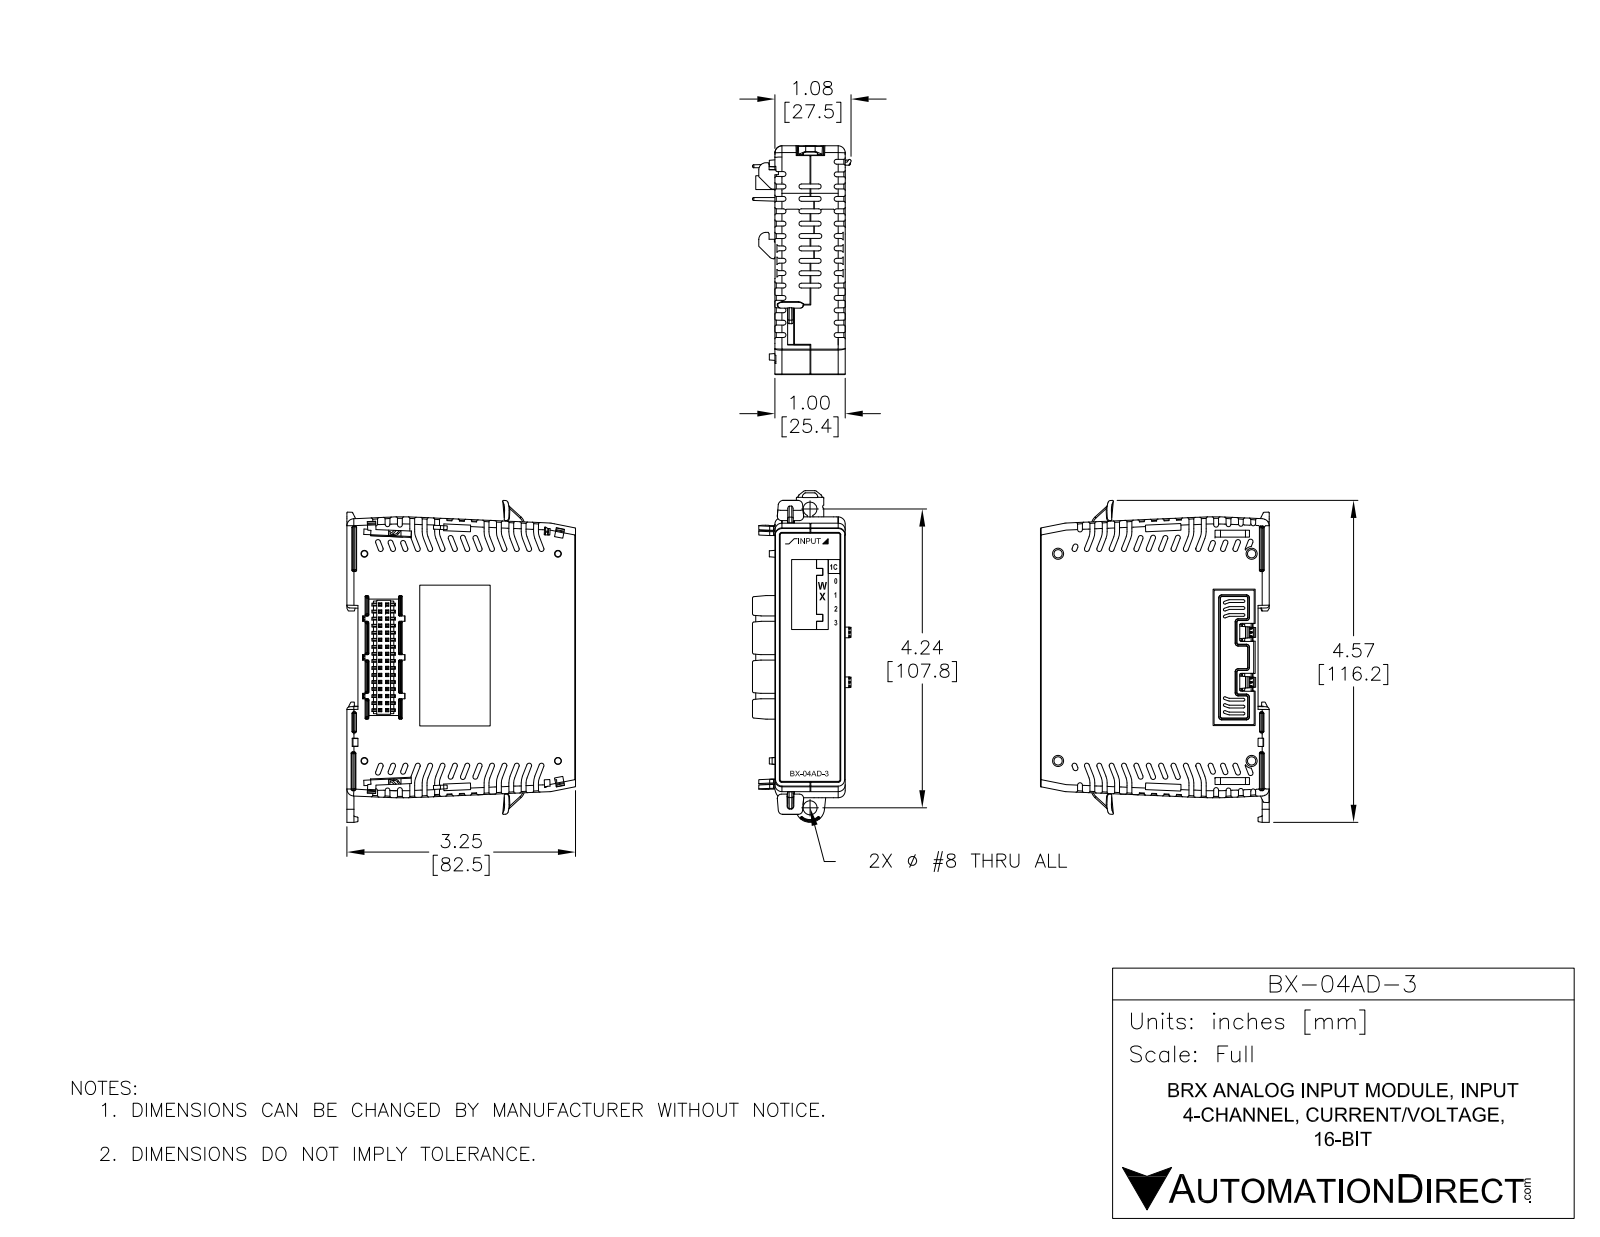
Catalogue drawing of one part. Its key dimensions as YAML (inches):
part_name: "BX-04AD-3"
step_written_by: "SolidWorks 2017 (AUTOMOTIVE_DESIGN)"
units: inches
bodies: {solids: 4, faces: 3474, planar: 2477, cylindrical: 573, other: 424}
overall_size: [4.586, 3.25, 1.402]
volume: 11.58
surface_area: 72.48
round_holes:
  - {diameter: 0.047, count: 2}
  - {diameter: 0.065, count: 2}
  - {diameter: 0.118, count: 2}
  - {diameter: 0.118, count: 2}
  - {diameter: 0.199, count: 1}
round_bosses_or_shafts:
  - {diameter: 0.062, count: 2}
  - {diameter: 0.059, count: 2}
partial_cylinders:
  - {radius: 0.005, count: 102}
  - {radius: 0.01, count: 47}
  - {radius: 0.008, count: 41}
  - {radius: 0.02, count: 34}
  - {radius: 0.005, count: 24}
  - {radius: 0.117, count: 14}
  - {radius: 0.039, count: 13}
  - {radius: 0.01, count: 12}
face_to_face_distances: [1, 3.211, 3.22, 0.475, 0.157, 3.053, 3.063, 0.1, 0.039, 0.787]
hole_center_spacings: [0.1, 0.824, 0.919, 1.3, 2.093, 2.193, 2.585, 2.617]
